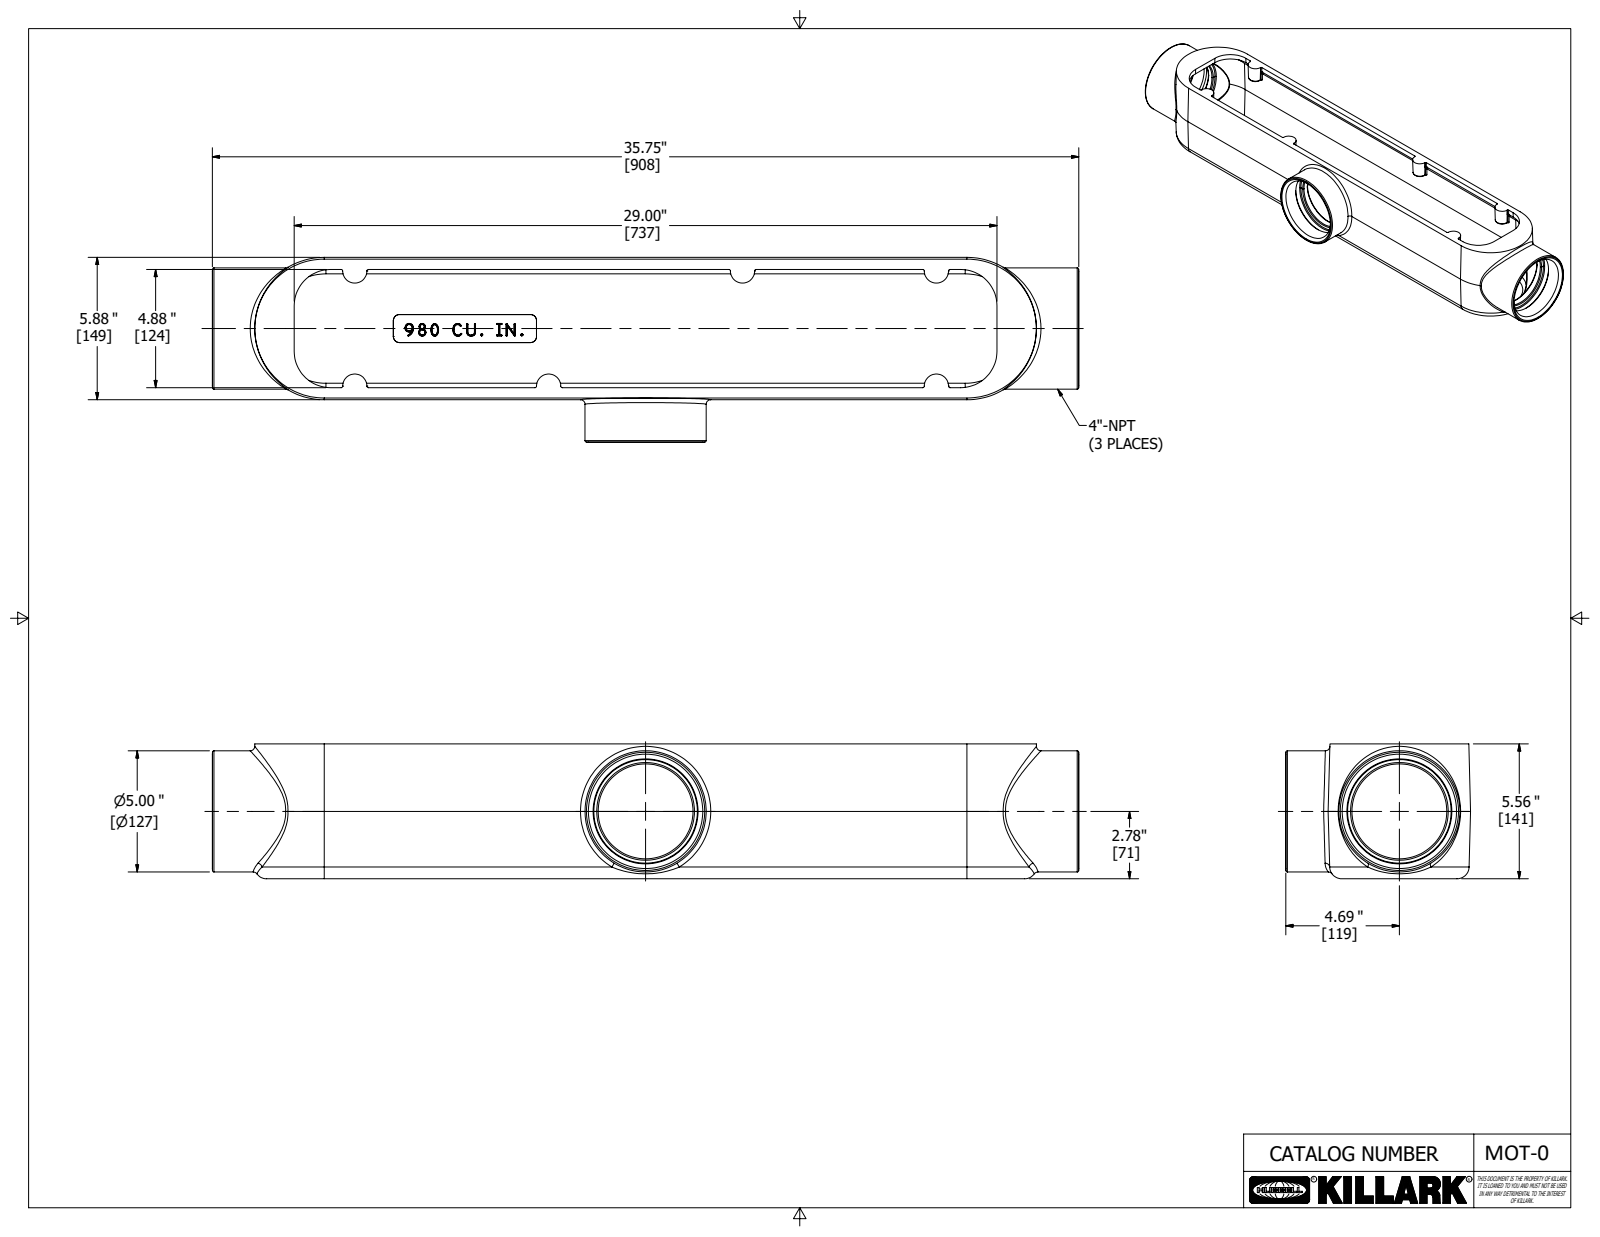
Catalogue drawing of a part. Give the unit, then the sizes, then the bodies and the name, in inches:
Units: inches
Overall size (bounding box): 35.75 × 7.625 × 5.563
Round holes (diameter × count): ⌀3.914 ×2, ⌀4.511 ×2
Round bosses / shafts (diameter × count): ⌀5 ×2
Partial cylindrical surfaces — rounded edges, fillets, slot ends (radius × count): R0.062 ×46, R0.25 ×2, R0.5 ×2, R2.25 ×1
Main face-to-face distances: 0.375, 0.375, 5.875, 5.5, 5.125, 5.5, 5.187, 5.562, 5.447, 5.072
Volume: 223.9 in³ · Surface area: 1 237 in²
Bodies: 1 solid, 646 faces (267 planar, 71 cylindrical, 308 other)
Part name (STEP PRODUCT): 21319
STEP written by: Autodesk Inventor 2020 (AUTOMOTIVE_DESIGN)
